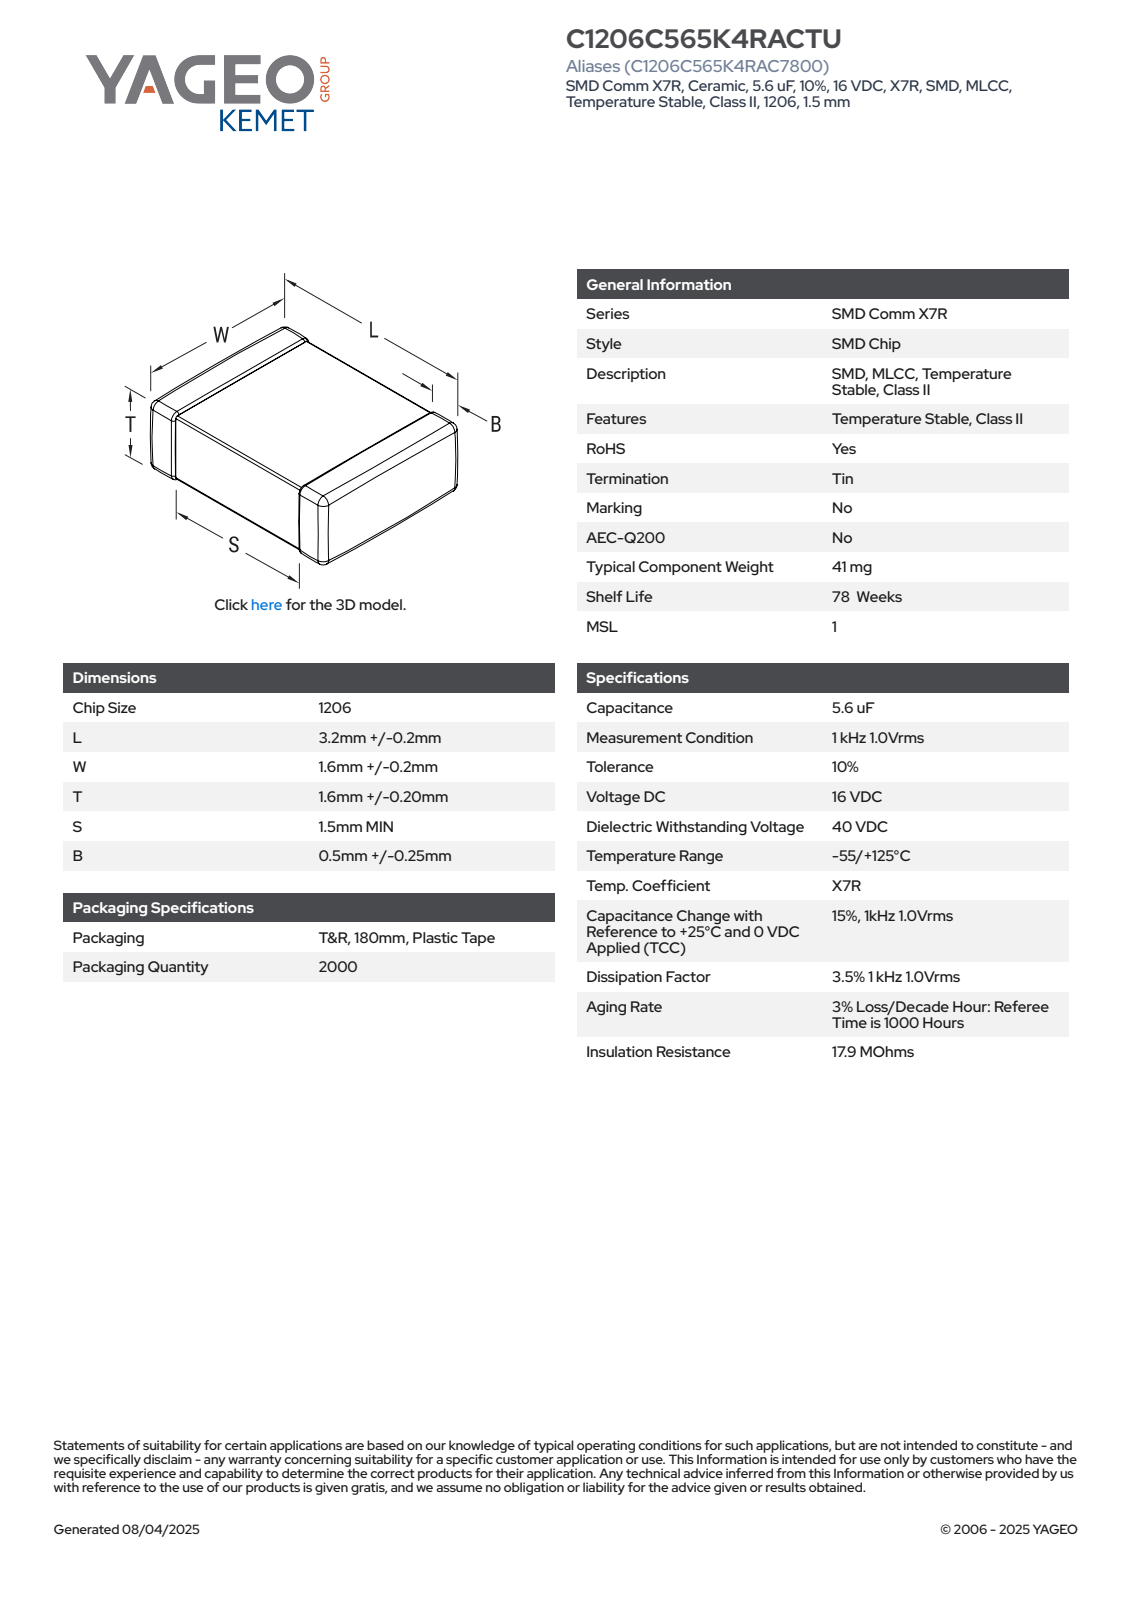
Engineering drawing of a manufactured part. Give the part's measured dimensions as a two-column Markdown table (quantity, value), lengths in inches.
| quantity | value |
| --- | --- |
| part name | CCS_CCSTD_1206_L3.4W1.8T1.8B0.5 |
| STEP written by | SolidWorks 2021 (AUTOMOTIVE_DESIGN) |
| units | inches |
| bodies | 4 solids, 125 faces (71 planar, 38 cylindrical, 16 other) |
| overall size | 0.134 × 0.071 × 0.071 |
| volume | 0.001 in³ |
| surface area | 0.048 in² |
| main face-to-face distances | 0.069, 0.068, 0.071, 0.134, 0.068, 0.07, 0.062, 0.072, 0.072, 0.061 |
